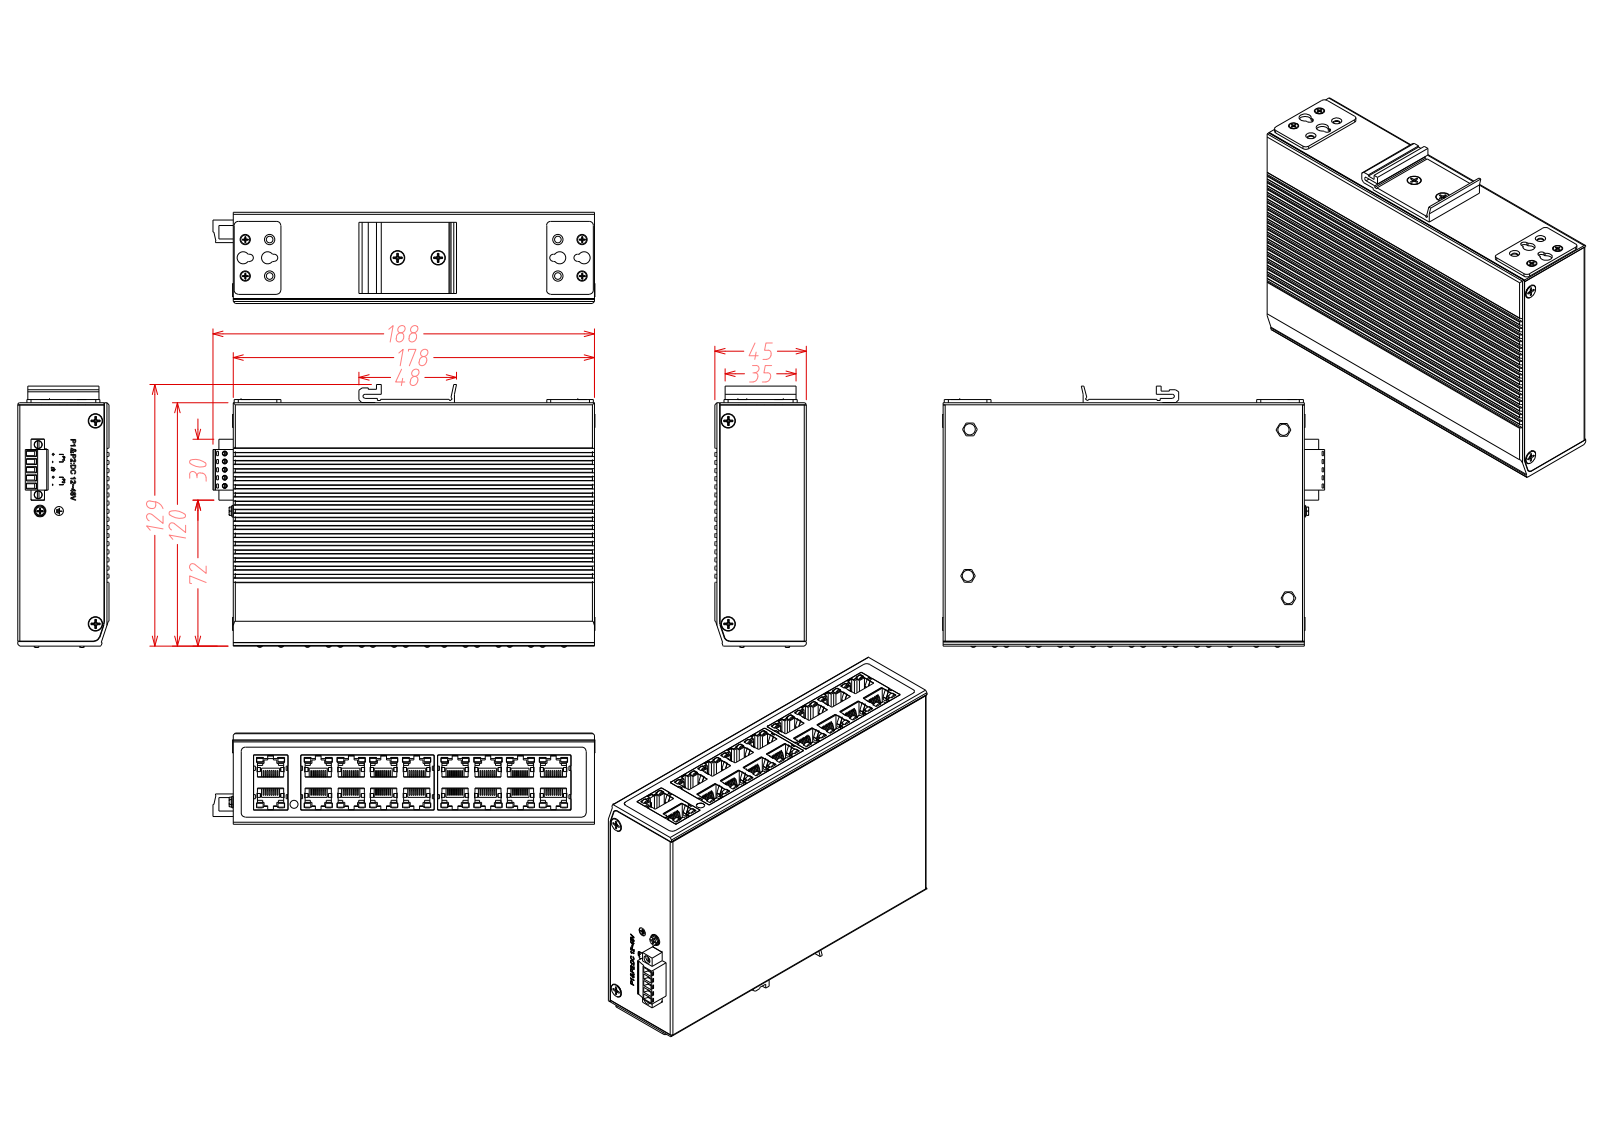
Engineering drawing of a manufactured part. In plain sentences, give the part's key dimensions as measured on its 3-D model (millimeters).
The part is named "PRT0266; PRT0267; PRT0268; PRT0269 (+8 more)". Its 3-D file was written by "PRO/ENGINEER BY PARAMETRIC TECHNOLOGY CORPORATION, 2011310 (CONFIG_CONTROL_DESIGN)". It is 65 solids with 3955 faces: 3154 planar, 627 cylindrical and 174 other. Overall it measures 188.25 by 128.7 by 45 millimeters. Its volume is 172 155 cubic millimeters and its surface area 187 667 square millimeters. Round holes: 13 of diameter 2.5, 8 of diameter 3.3, 6 of diameter 4, 5 of diameter 2.4, 4 of diameter 5.5, 4 of diameter 6, 2 of diameter 2.2, 2 of diameter 3.6, 1 of diameter 4.3. Round bosses or shafts: 7 of diameter 3.7, 5 of diameter 2.16, 5 of diameter 2.05, 5 of diameter 1, 5 of diameter 0.2, 4 of diameter 5.4, 4 of diameter 2.29, 2 of diameter 3.8. Partial cylindrical surfaces (rounded edges, fillets, slot ends): 72 of radius 0.2, 18 of radius 1.89, 17 of radius 1, 13 of radius 2, 6 of radius 0.38, 6 of radius 0.5, 4 of radius 1.75, 2 of radius 0.63. The main face-to-face distances are 1, 44, 41.5, 40.5, 3.5, 45, 2.5, 177, 43, 178. The hole center spacings are 9.06, 12, 155.26, 4, 14.21, 15.81, 18, 21.63.
